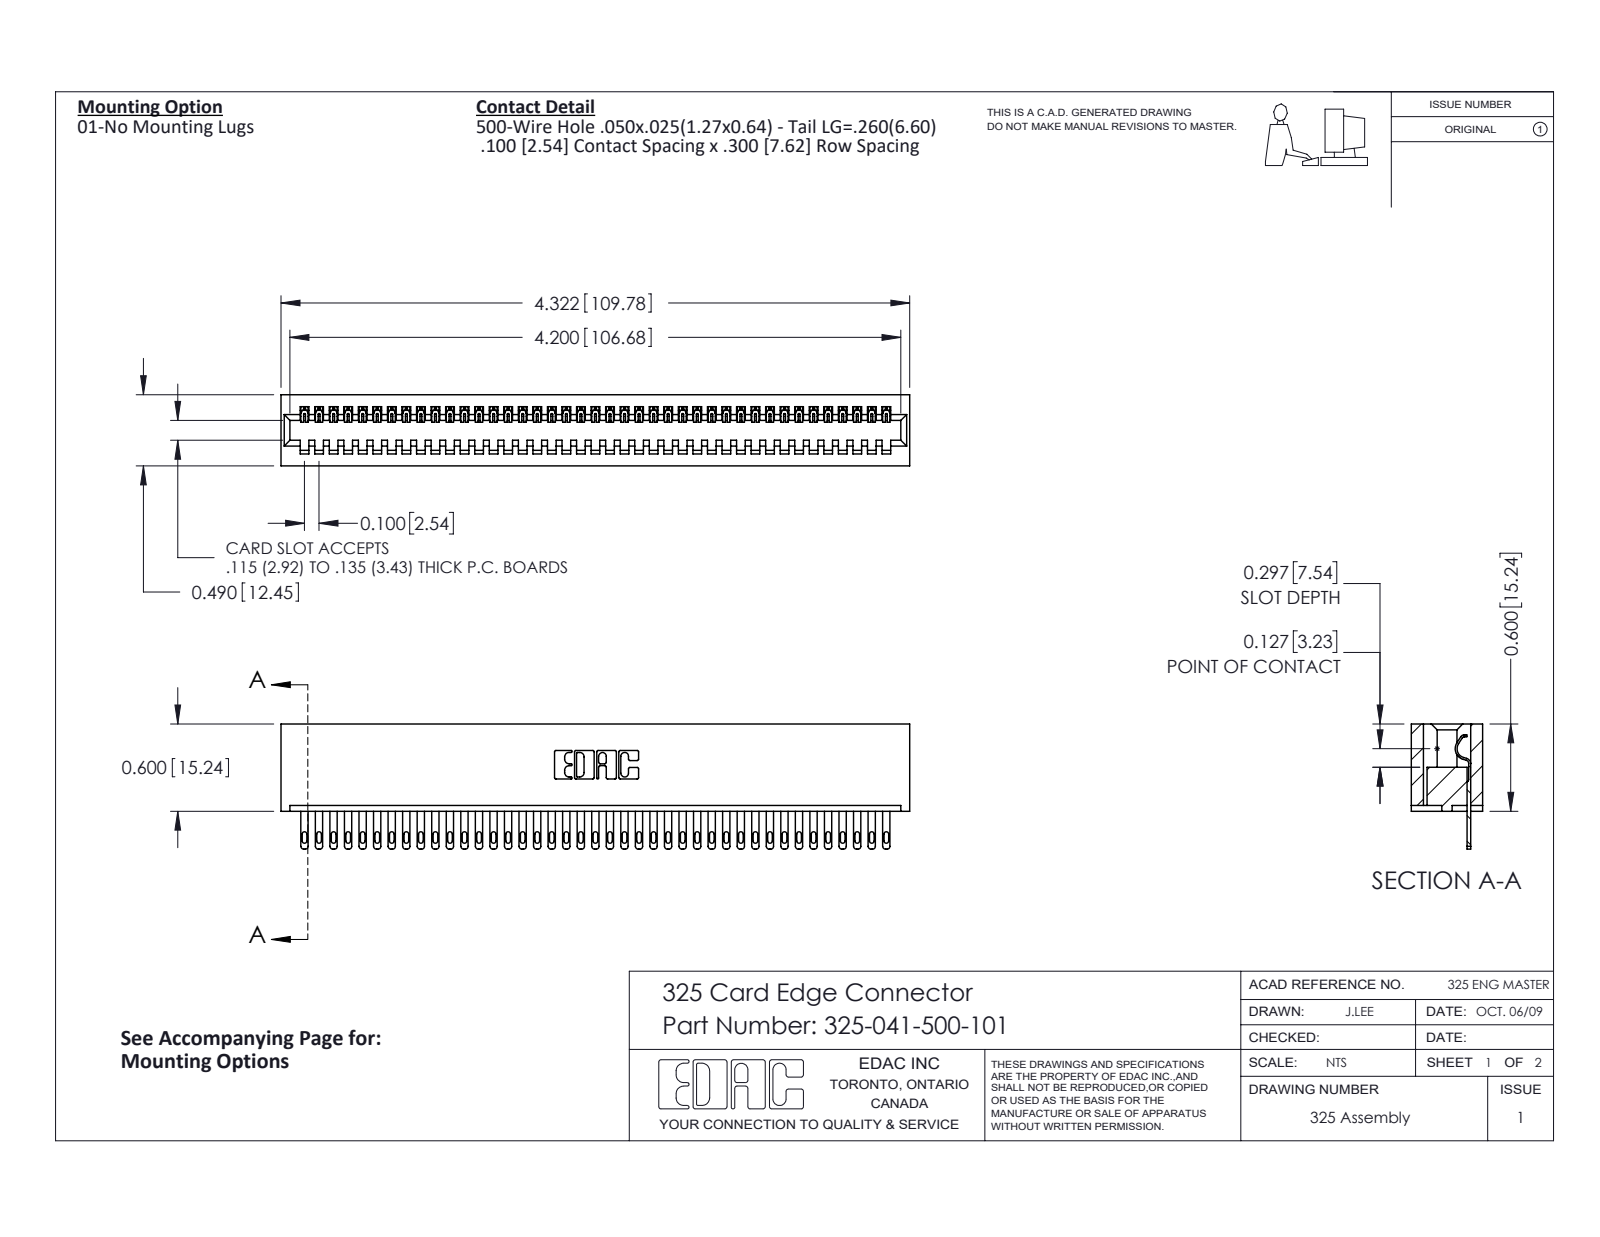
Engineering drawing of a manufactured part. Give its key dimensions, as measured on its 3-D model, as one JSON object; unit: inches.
{"part_name": "325-292-001_325-293-100; 325 Part_Lugless; 325-041-500-101", "step_written_by": "SolidWorks 2016 (CONFIG_CONTROL_DESIGN)", "units": "inches", "bodies": {"solids": 42, "faces": 2320, "planar": 1542, "cylindrical": 778, "other": 0}, "overall_size": [4.322, 0.86, 0.49], "volume_in3": 0.886, "surface_area_in2": 25.48, "partial_cylinders_radius": [[0.006, 82], [0.016, 82], [0.02, 82], [0.01, 22], [0.007, 6], [0.031, 6], [0.026, 3], [0.014, 1]], "face_to_face_distances": [0.083, 0.407, 0.3, 0.49, 0.107, 0.383, 0.025, 0.325, 0.56, 0.263]}
